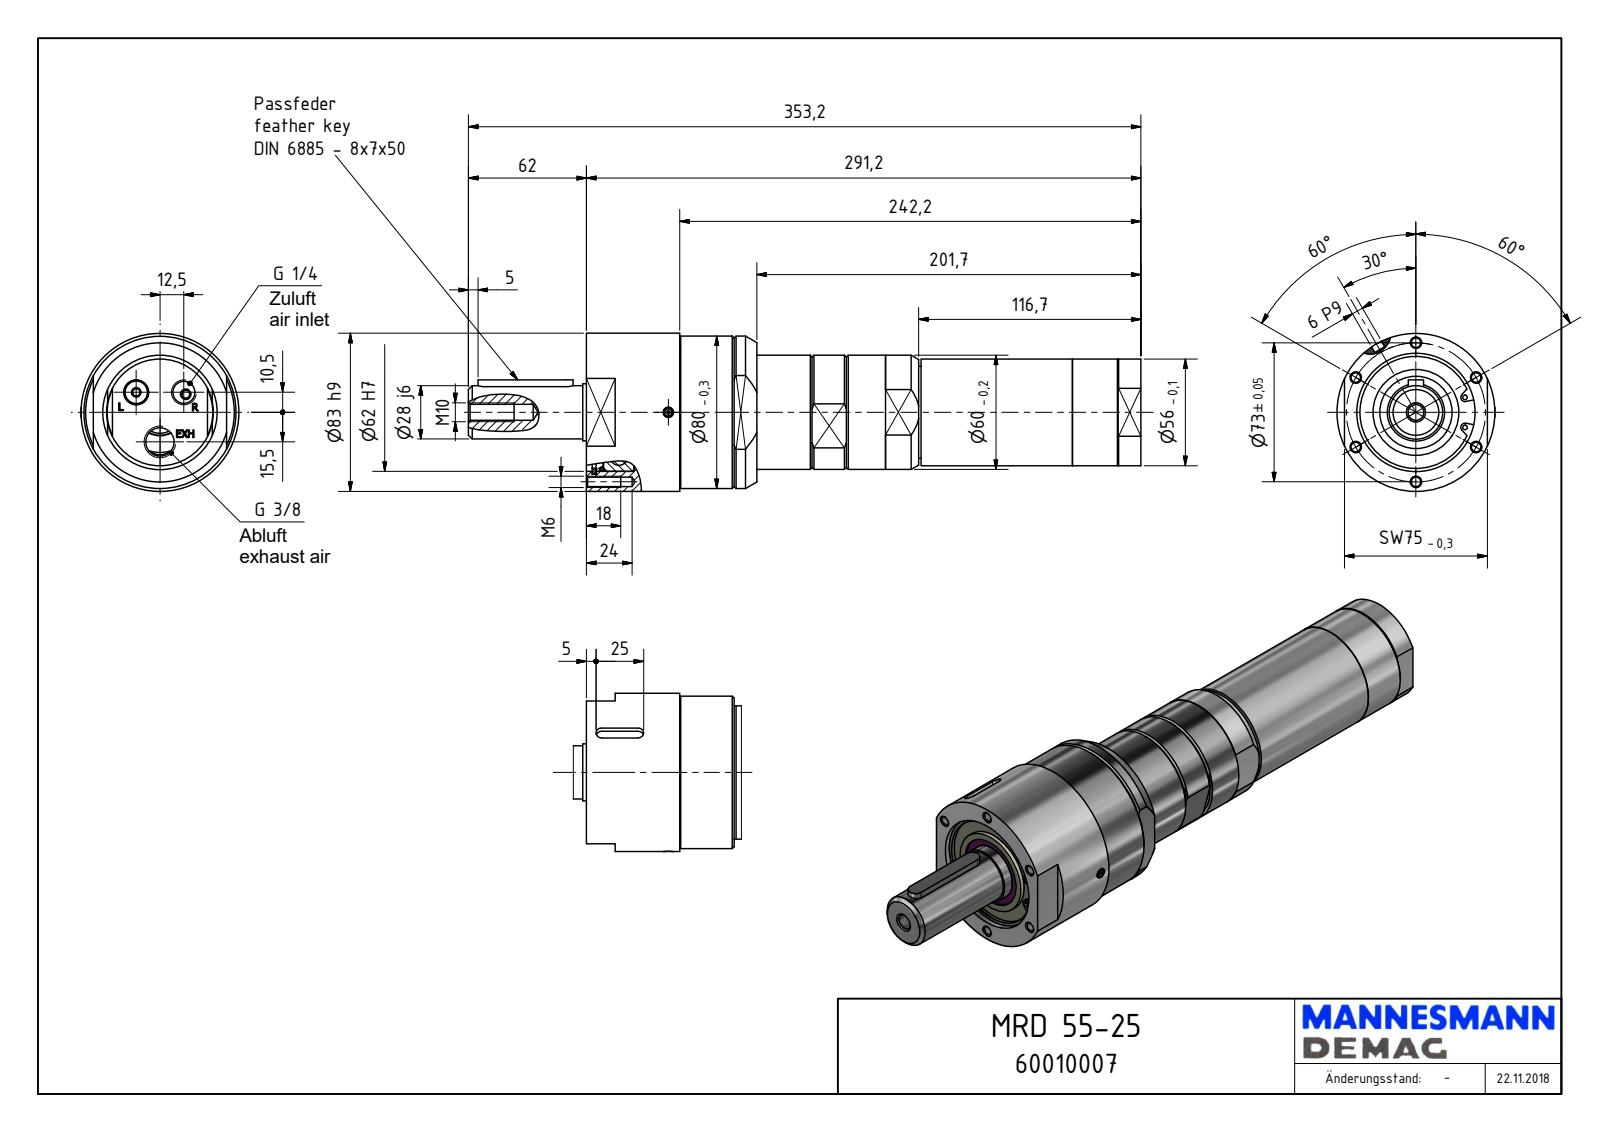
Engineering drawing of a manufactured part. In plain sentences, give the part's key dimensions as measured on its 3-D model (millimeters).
The part is named "MRD 55-25_60010007". Its 3-D file was written by "Autodesk Inventor 2018 (AUTOMOTIVE_DESIGN)". It is 1 solid with 334 faces: 166 planar, 97 cylindrical and 71 other. Overall it measures 353.2 by 83 by 83 millimeters. Its volume is 1 000 000 cubic millimeters and its surface area 99 904 square millimeters. Round holes: 6 of diameter 4.92, 3 of diameter 1.55, 3 of diameter 4, 2 of diameter 2.5, 2 of diameter 5.5, 1 of diameter 8.38, 1 of diameter 11.45, 1 of diameter 14.95, 1 of diameter 36.5, 1 of diameter 38, 1 of diameter 40, 1 of diameter 58.69. Round bosses or shafts: 2 of diameter 5, 2 of diameter 3.6, 1 of diameter 83, 1 of diameter 80, 1 of diameter 68.18, 1 of diameter 67, 1 of diameter 60, 1 of diameter 56. Partial cylindrical surfaces (rounded edges, fillets, slot ends): 6 of radius 10, 2 of radius 2.25, 2 of radius 3, 2 of radius 4, 2 of radius 6, 1 of radius 5.72, 1 of radius 20.29, 1 of radius 21.78. The main face-to-face distances are 2.5, 291.2, 49, 242.2, 0.5, 10, 62.5, 201.7, 89.5, 40.5. The hole center spacings are 36.5, 63.22, 28.85, 73, 11.89, 16.32, 20.62, 26.77.
